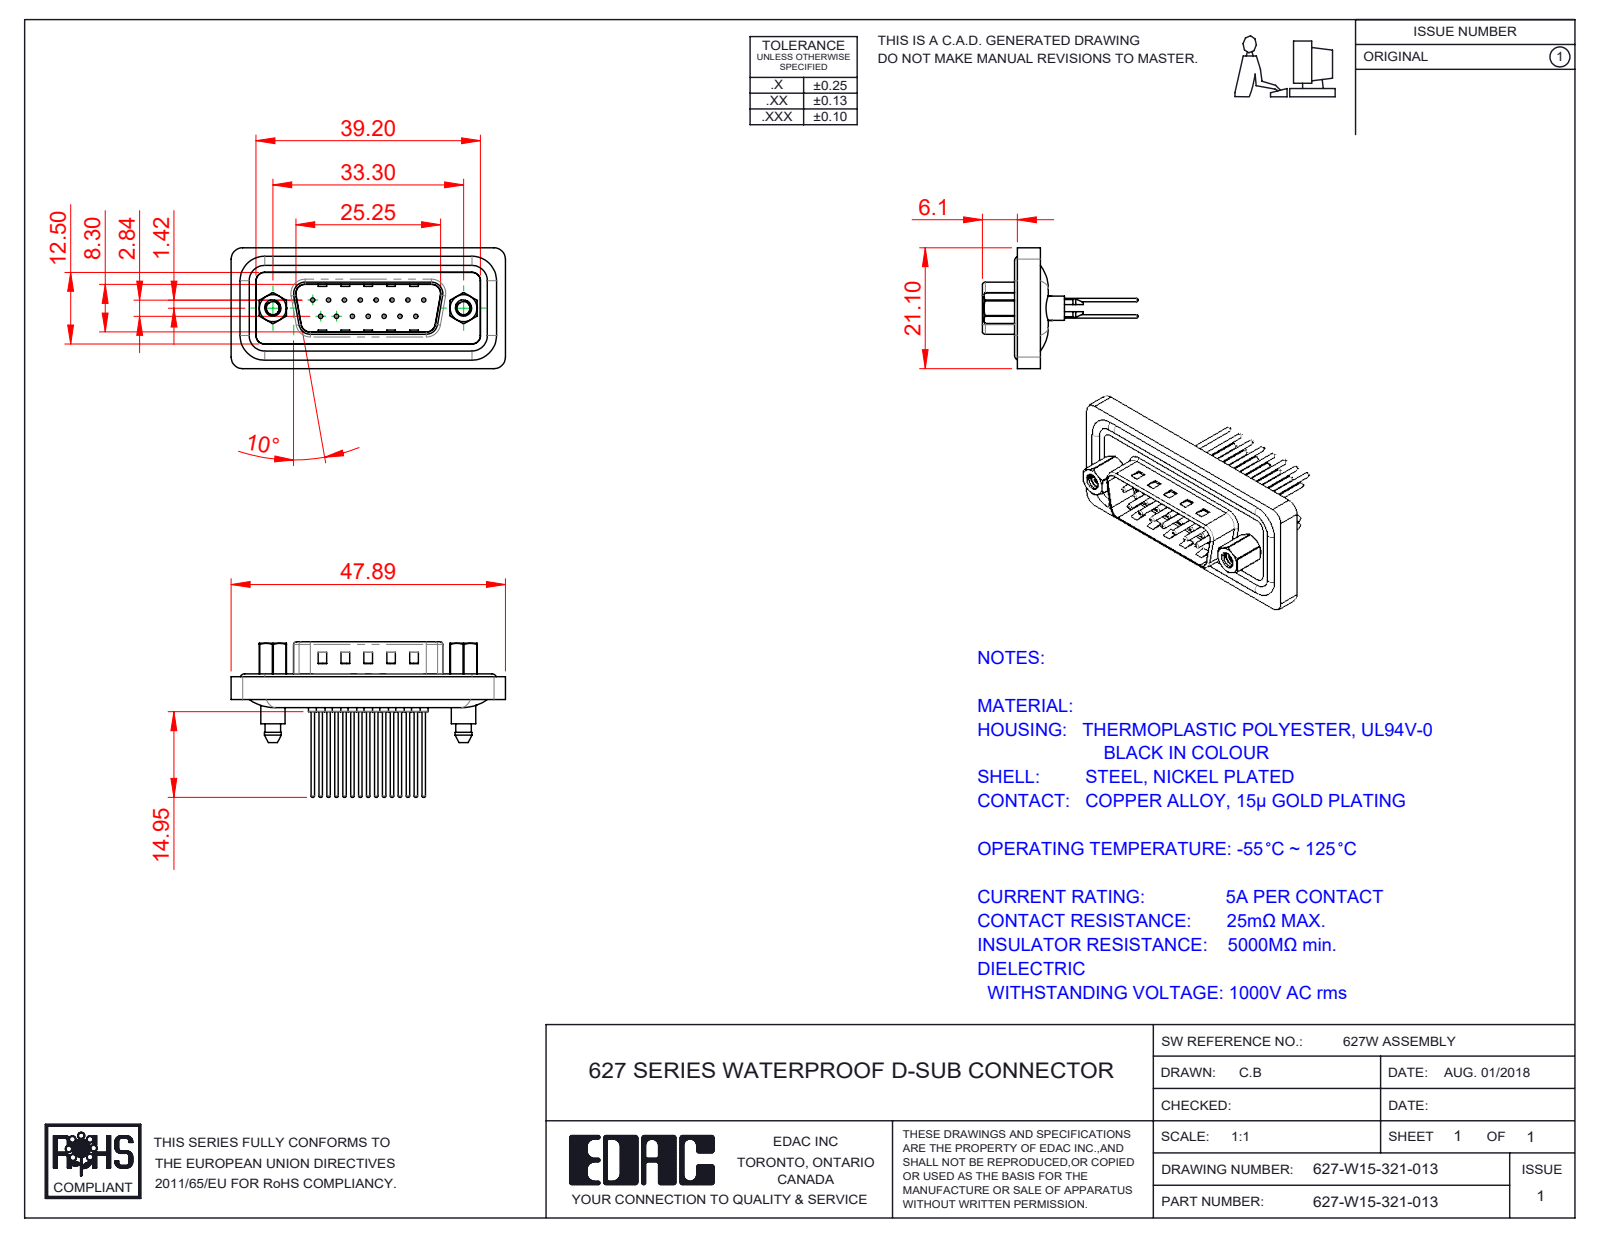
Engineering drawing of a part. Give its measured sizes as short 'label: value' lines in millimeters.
name: 627W Housing_15 Contacts; 627W Waterproof Housing_15 Contacts BL; 627-W15-321-013; 627W Contact Row 2_21 (+4 more)
written by: SolidWorks 2020 (CONFIG_CONTROL_DESIGN)
unit: mm
bodies: 23 solids, 1115 faces (292 planar, 484 cylindrical, 339 other)
size: 47.89 × 27.15 × 21.1
volume: 4 989 mm³; area: 8 543 mm²
holes: 15× ⌀0.75, 15× ⌀1.5, 15× ⌀1.6, 15× ⌀2, 2× ⌀2.26, 2× ⌀2.29, 2× ⌀4, 2× ⌀4.25, 2× ⌀4.8
bosses: 15× ⌀0.6, 4× ⌀1.6, 2× ⌀5.4, 2× ⌀4.9, 2× ⌀2.79, 1× ⌀4.25, 1× ⌀1.5
rounds: 14× R1.5, 12× R2, 8× R0.5, 6× R1.6, 4× R0.9, 4× R2.7, 4× R4.3, 2× R0.4
face distances: 0.4, 1.1, 1.6, 2.5, 2.9, 5.65, 4.1, 4.5, 0.5, 15.45
hole spacings: 3.16, 2.77, 5.54, 8.31, 5.03, 11.08, 5.04, 7.48
